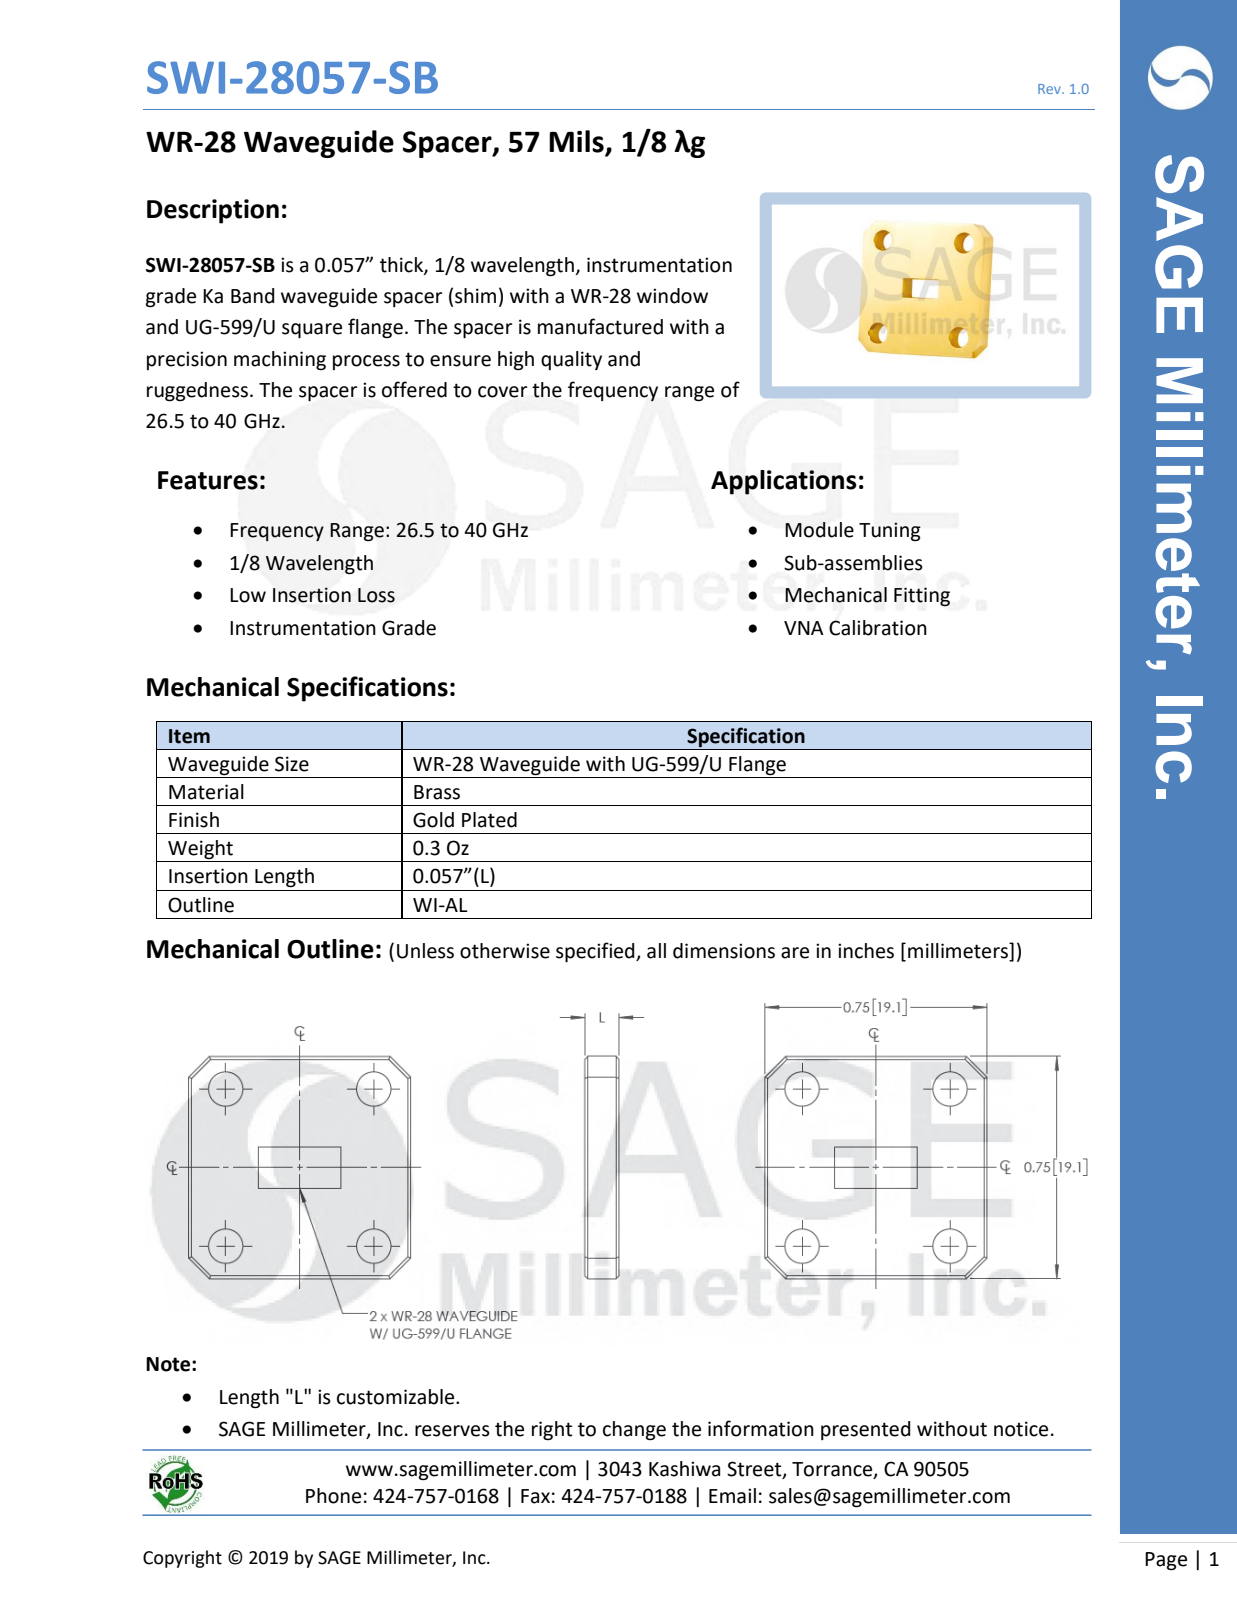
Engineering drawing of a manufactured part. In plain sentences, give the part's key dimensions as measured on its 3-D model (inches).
The part is named "SWI-28057-SB". Its 3-D file was written by "SolidWorks 2016 (CONFIG_CONTROL_DESIGN)". It is 1 solid with 38 faces: 30 planar, 8 cylindrical and 0 other. Overall it measures 0.75 by 0.75 by 0.057 inches. Its volume is 0.027 cubic inches and its surface area 1.202 square inches. Round holes: 4 of diameter 0.116. The main face-to-face distances are 0.057, 0.556, 0.305, 0.445, 0.75, 0.75, 0.235, 0.515, 0.14, 0.28. The hole center spacings are 0.5, 0.53, 0.729.
